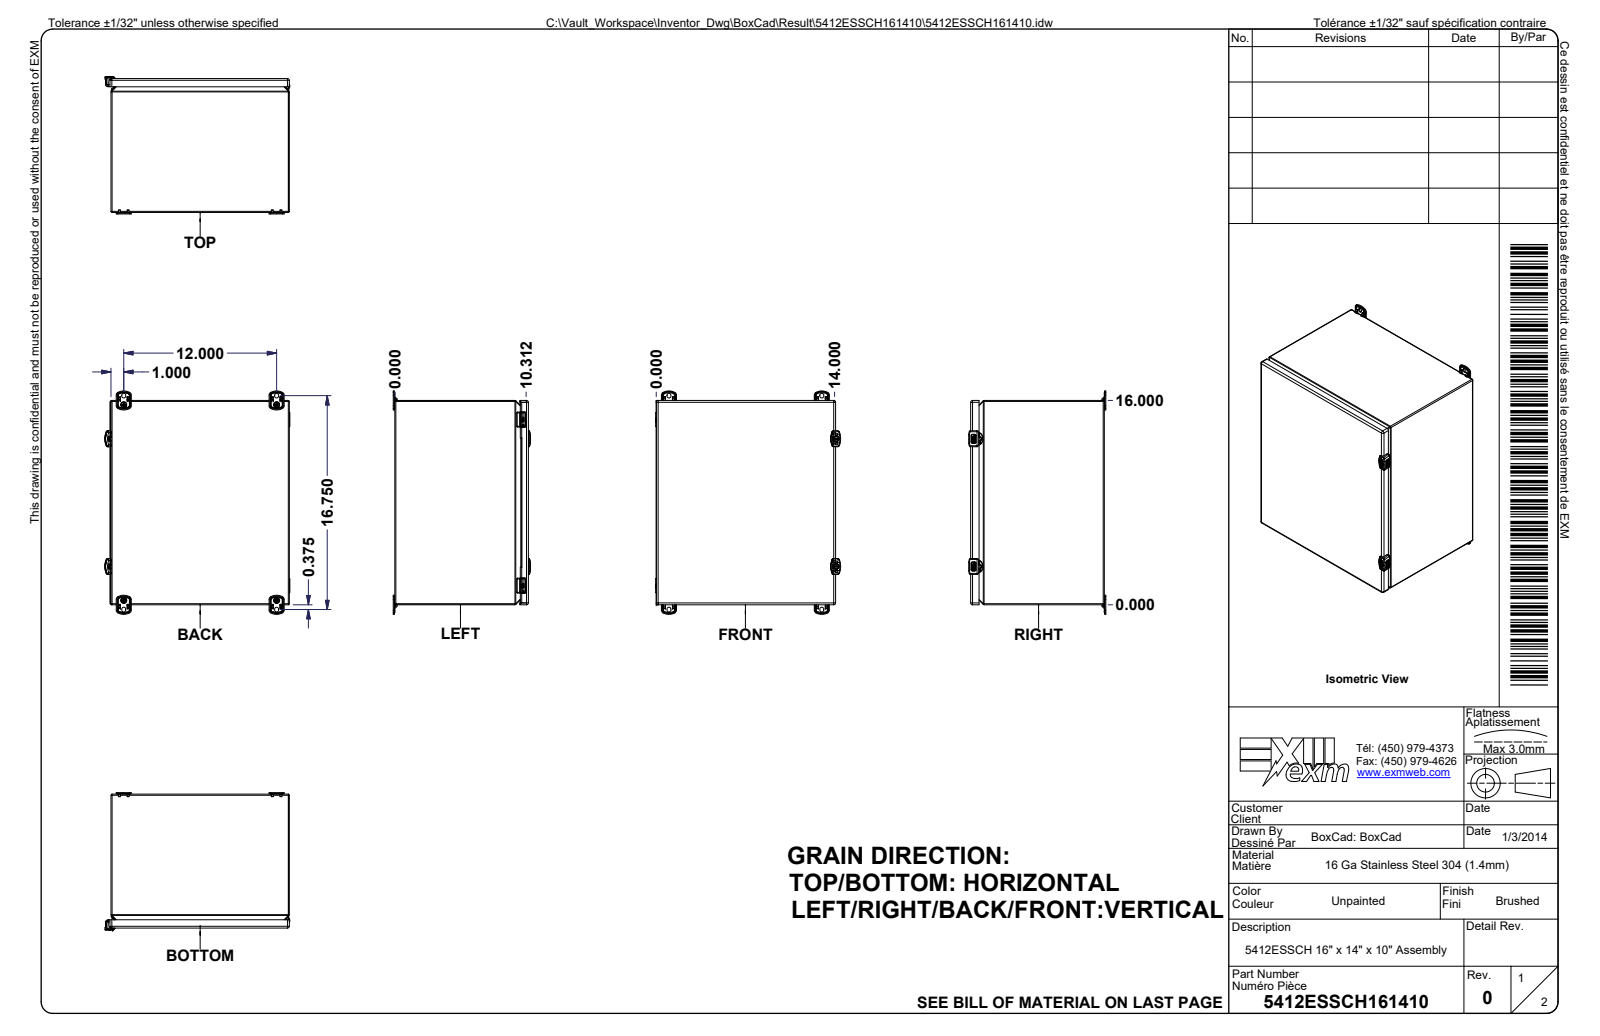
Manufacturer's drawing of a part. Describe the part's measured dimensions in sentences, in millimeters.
The part is named "5412ESSCH161410; 5412ESSCH161410B; 5412ESSCH161410B-P; STK-Q-08500 (+8 more)". Its 3-D file was written by "Autodesk Inventor 2024 (AUTOMOTIVE_DESIGN)". It is 47 solids with 7453 faces: 3549 planar, 1558 cylindrical and 2346 other. Overall it measures 444.4 by 366.8 by 273.2 millimeters. Its volume is 1 255 000 cubic millimeters and its surface area 1 770 000 square millimeters. Round holes: 7 of diameter 5.1, 6 of diameter 0.8, 6 of diameter 6.1, 4 of diameter 5, 4 of diameter 7.9, 4 of diameter 8.1, 2 of diameter 4.2, 2 of diameter 4.4, 2 of diameter 5.5, 2 of diameter 6, 2 of diameter 10.7, 1 of diameter 3.2. Round bosses or shafts: 8 of diameter 5.9, 6 of diameter 10, 6 of diameter 0.9, 4 of diameter 13, 4 of diameter 12.7, 3 of diameter 5, 2 of diameter 10.5, 2 of diameter 8.4. Partial cylindrical surfaces (rounded edges, fillets, slot ends): 252 of radius 0.2, 97 of radius 0.5, 84 of radius 0.1, 83 of radius 0.3, 56 of radius 1, 44 of radius 0.3, 34 of radius 0.8, 27 of radius 1.5. The main face-to-face distances are 1.3, 264.9, 354.3, 405.1, 263.5, 266.2, 11.4, 253.5, 13.1, 10. The hole center spacings are 485.6, 13.9, 375.4, 308.3, 311.2, 362, 362, 59.2.
